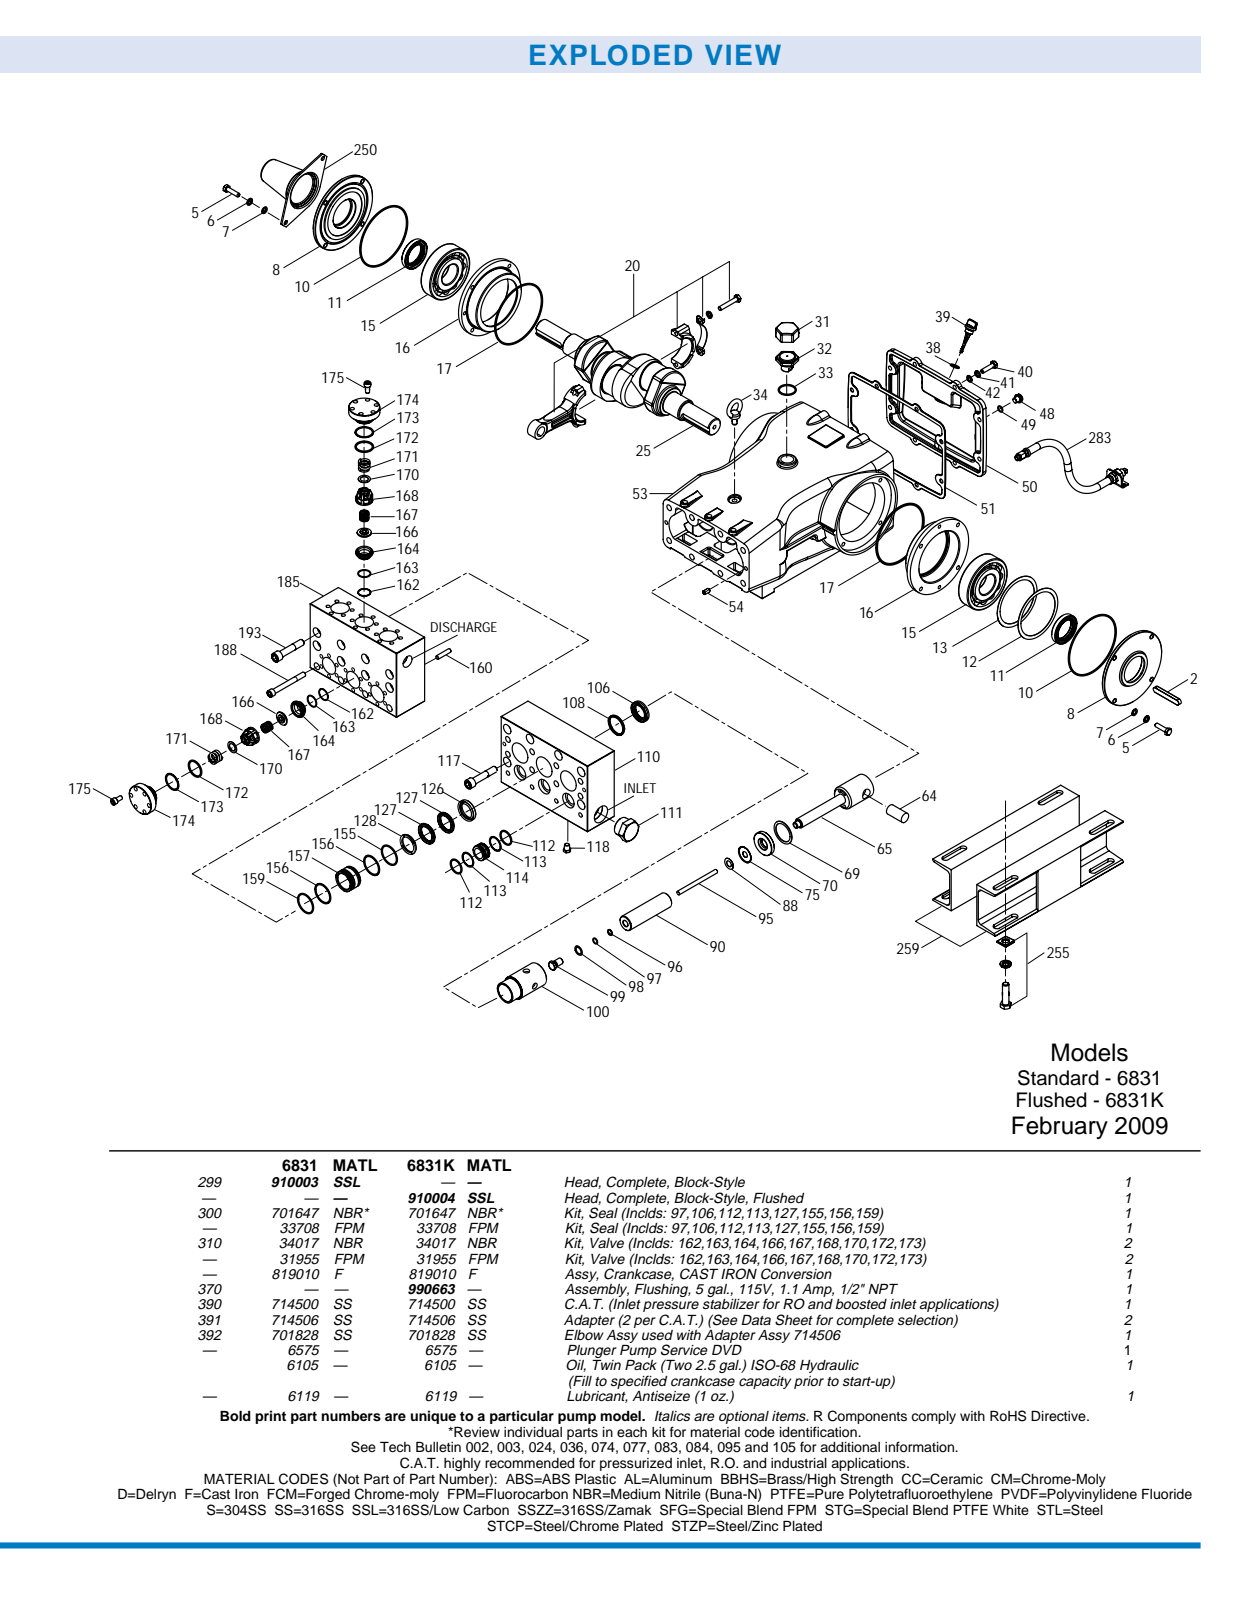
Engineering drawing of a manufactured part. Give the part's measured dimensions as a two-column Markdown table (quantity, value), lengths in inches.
| quantity | value |
| --- | --- |
| part name | Socket Head Cap Screw_AM_B18.3.1M - 10 x 1.5 x 30 Hex SHCS -- 30NHX; 701116; 701321; Socket Head Cap Screw_AM_B18.3.1M - 16 x 2.0 x 110 Hex SHCS 44NHX (+8 more) |
| STEP written by | SolidWorks 2007 (AUTOMOTIVE_DESIGN) |
| units | inches |
| bodies | 116 solids, 3240 faces (1424 planar, 833 cylindrical, 983 other) |
| overall size | 29.723 × 24.016 × 12.007 |
| volume | 2 878 in³ |
| surface area | 2 892 in² |
| round holes (diameter × count) | 0.413 × 36, 0.551 × 20, 0.689 × 18, 1.024 × 18, 0.402 × 16, 0.335 × 13, 0.425 × 12, 0.438 × 12, 1.22 × 6, 0.438 × 3, 1.457 × 3, 1.8 × 3 |
| round bosses / shafts (diameter × count) | 0.63 × 66, 0.394 × 48, 0.945 × 18, 0.787 × 12, 0.724 × 12, 1.772 × 7, 3.051 × 6, 1.575 × 6 |
| partial cylindrical surfaces (radius × count) | 0.394 × 15, 0.197 × 13, 0.157 × 6, 0.294 × 4, 0.41 × 4, 0.51 × 4, 0.079 × 2, 0.276 × 2 |
| main face-to-face distances | 3.74, 3.937, 7.677, 1.454, 13.423, 2.204, 12.673, 0.75, 11.219, 0.709 |
| hole center spacings | 1.22, 4.095, 3.346, 2.114, 1.22, 2.441, 5.284, 3.958 |
